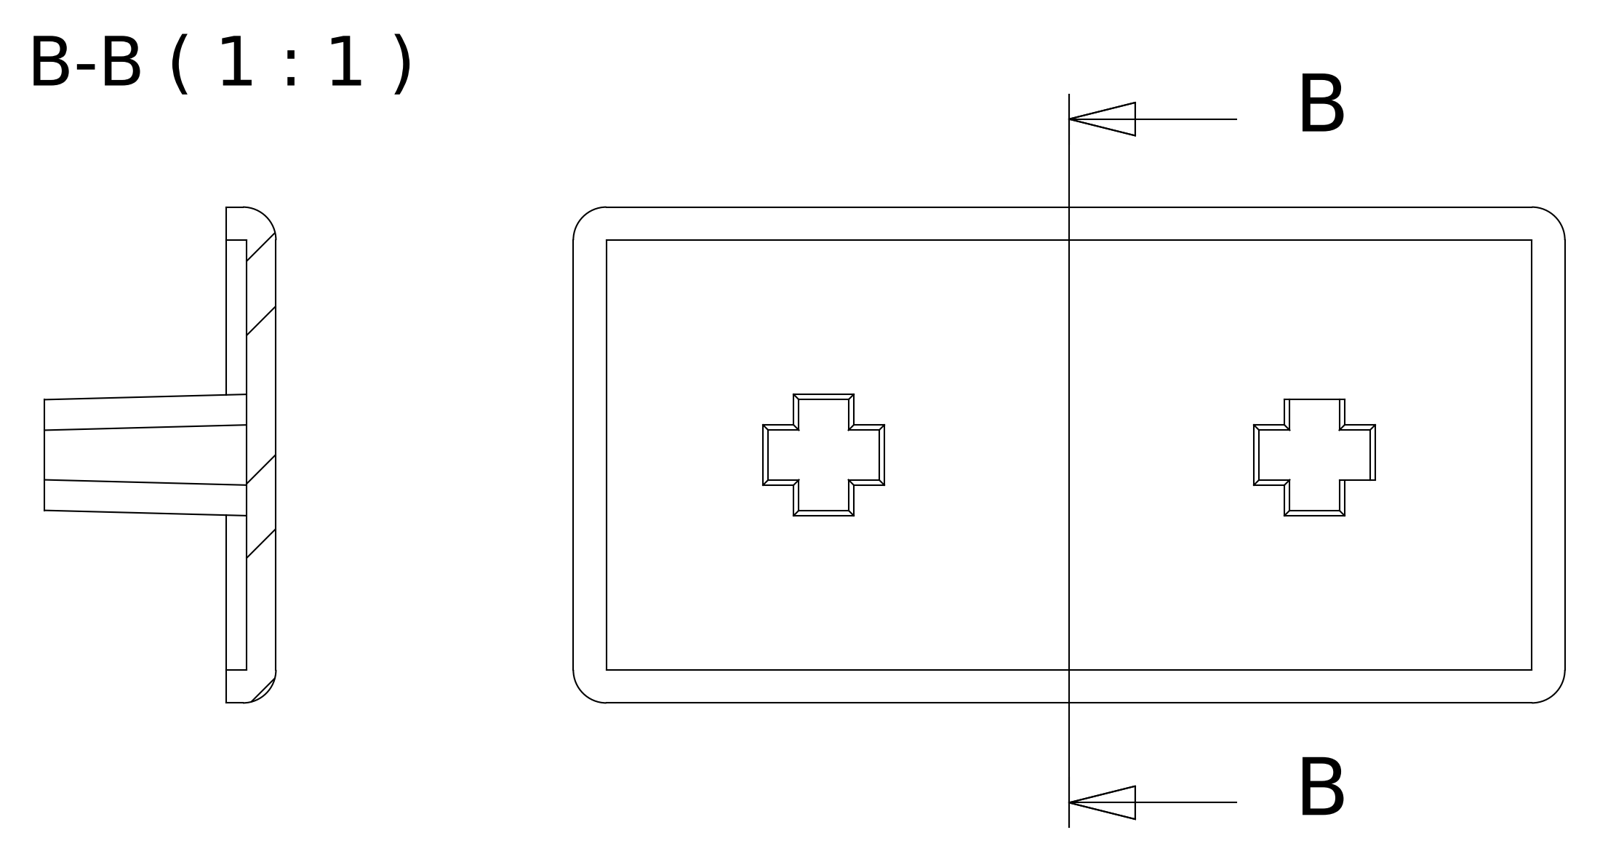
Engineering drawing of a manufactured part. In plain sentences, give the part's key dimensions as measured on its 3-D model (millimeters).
The part is named "DTPTR0000024". Its 3-D file was written by "Autodesk Inventor 2016 (AUTOMOTIVE_DESIGN)". It is 1 solid with 49 faces: 37 planar, 8 cylindrical and 4 other. Overall it measures 60 by 30 by 14 millimeters. Its volume is 4 352 cubic millimeters and its surface area 4 832 square millimeters. Partial cylindrical surfaces (rounded edges, fillets, slot ends): 8 of radius 2. The main face-to-face distances are 1.8, 1.2, 3, 1.85, 29.7, 2, 28, 27.85, 31.55, 26.
